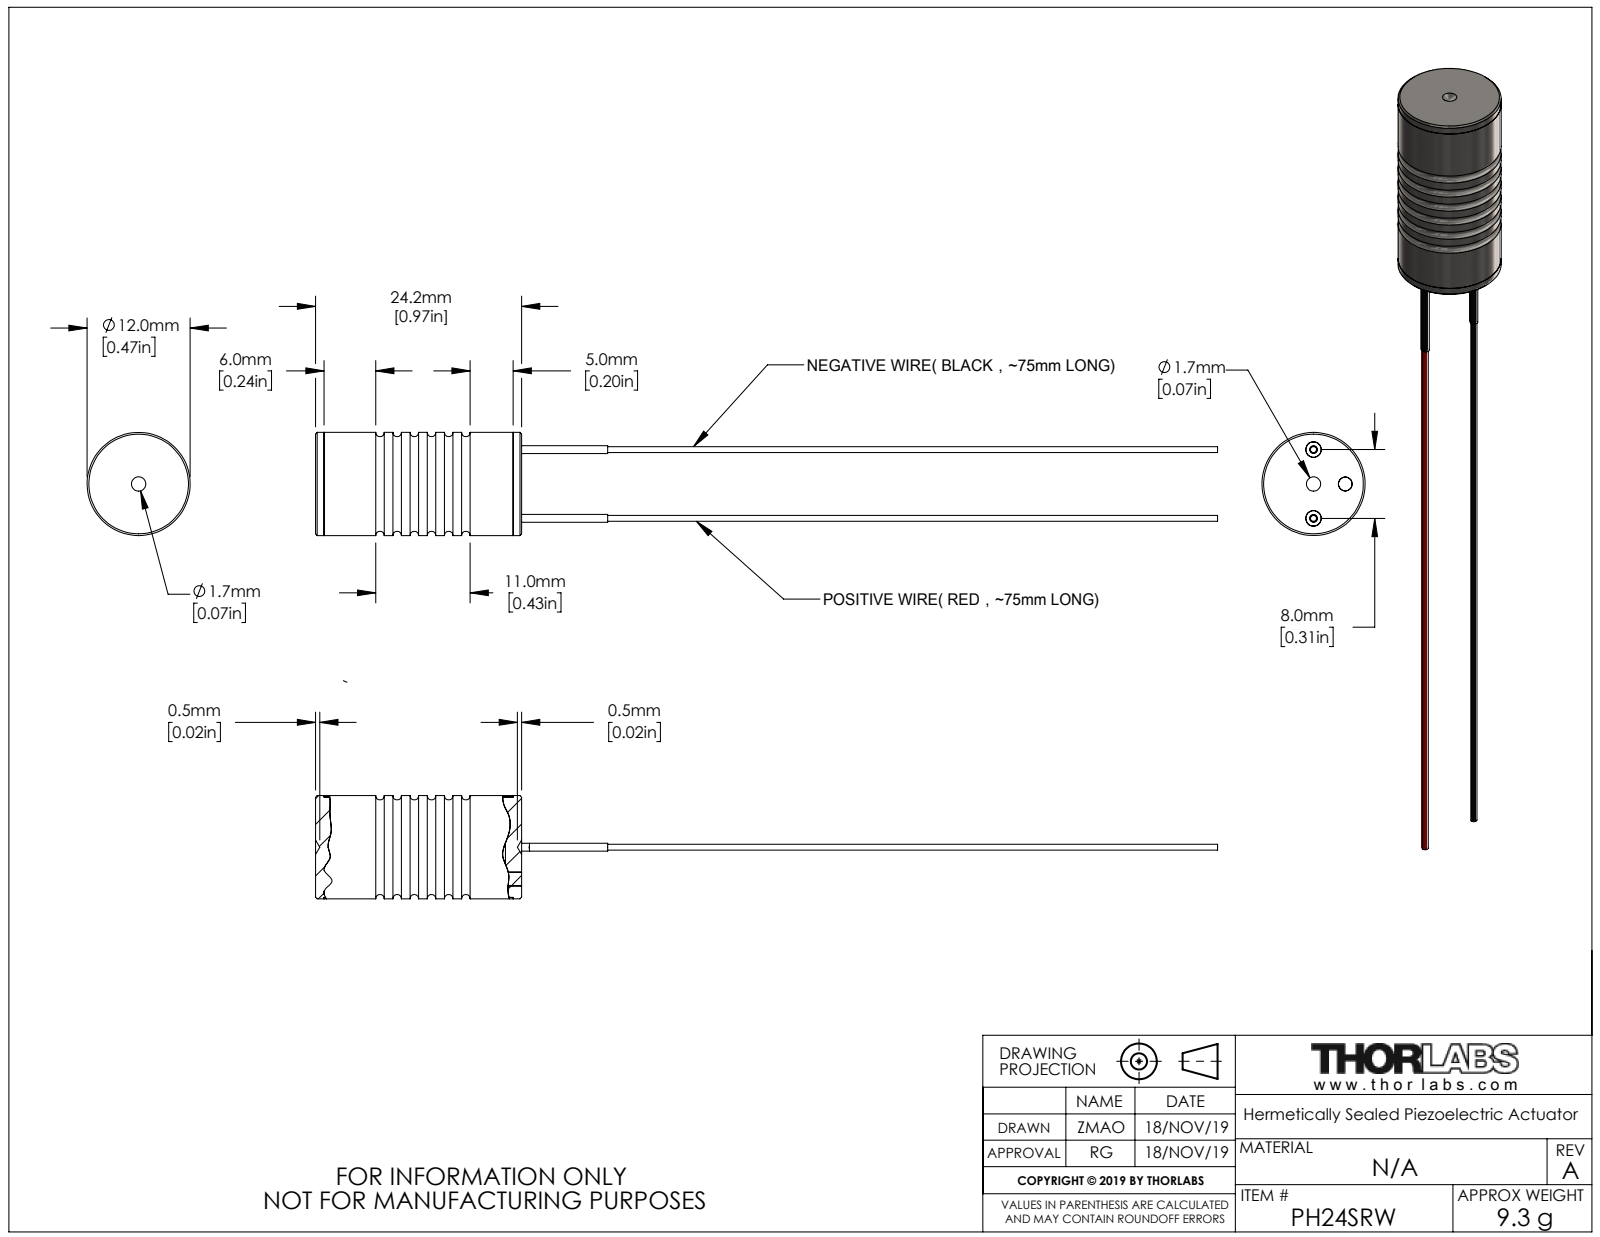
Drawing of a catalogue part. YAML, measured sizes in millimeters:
part_name: "CTN014895"
step_written_by: "SolidWorks 2018 (AUTOMOTIVE_DESIGN)"
units: millimeters
bodies: {solids: 12, faces: 181, planar: 33, cylindrical: 78, other: 70}
overall_size: [105, 12, 12]
volume: 820
surface_area: 3248
round_holes:
  - {diameter: 0.8, count: 2}
  - {diameter: 1.8, count: 2}
  - {diameter: 1.6, count: 1}
  - {diameter: 8, count: 1}
  - {diameter: 10, count: 1}
  - {diameter: 11.7, count: 1}
round_bosses_or_shafts:
  - {diameter: 0.9, count: 2}
  - {diameter: 0.7, count: 2}
  - {diameter: 12, count: 1}
partial_cylinders:
  - {radius: 0.25, count: 4}
face_to_face_distances: [2, 24, 20, 22, 4, 2.2, 17.8, 19.8, 21.8, 1]
hole_center_spacings: [4, 5.45, 3.7, 8]
